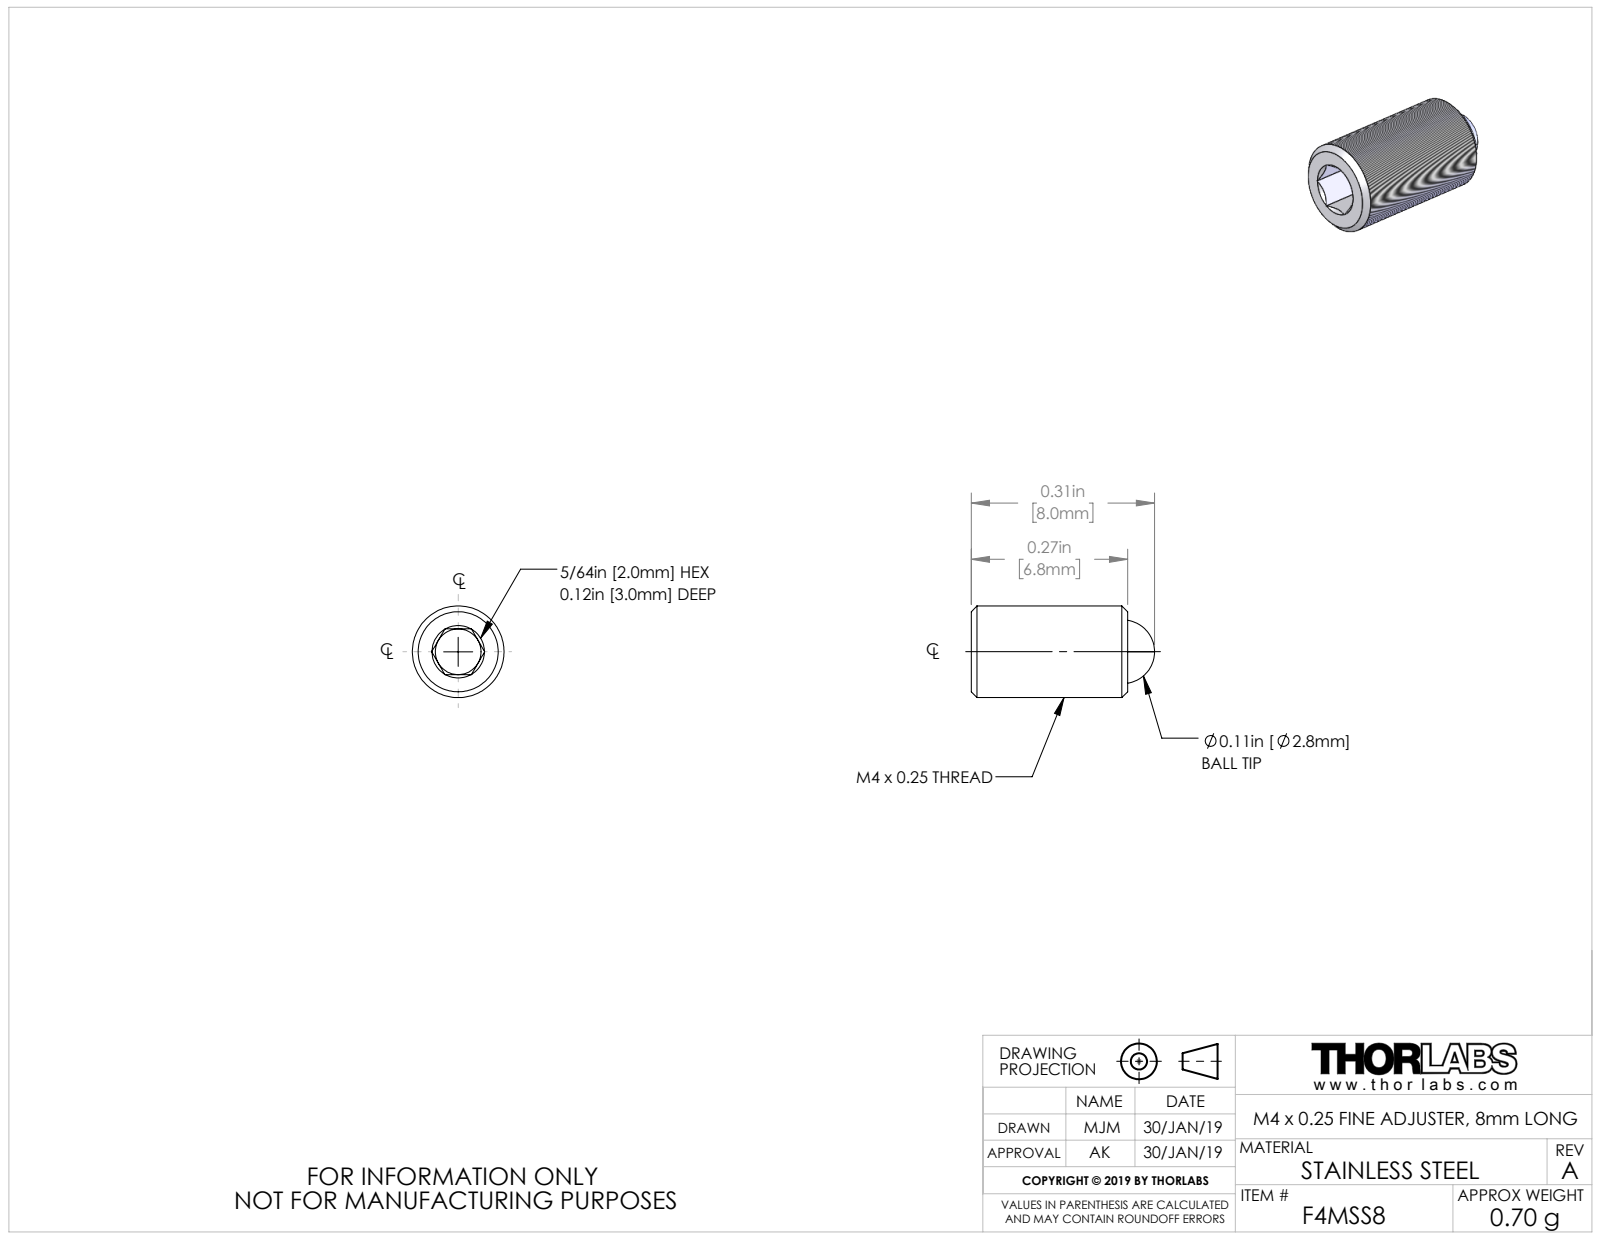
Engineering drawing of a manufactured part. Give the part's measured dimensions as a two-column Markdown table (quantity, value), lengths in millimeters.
| quantity | value |
| --- | --- |
| part name | TTN174694-E0W |
| STEP written by | SolidWorks 2018 (AUTOMOTIVE_DESIGN) |
| units | millimeters |
| bodies | 2 solids, 34 faces (9 planar, 6 cylindrical, 19 other) |
| overall size | 8 × 4 × 4 |
| volume | 80 mm³ |
| surface area | 168 mm² |
| round holes (diameter × count) | 2 × 1, 2.8 × 1 |
| round bosses / shafts (diameter × count) | 4 × 1 |
| main face-to-face distances | 2, 6.8, 3.8, 3 |
